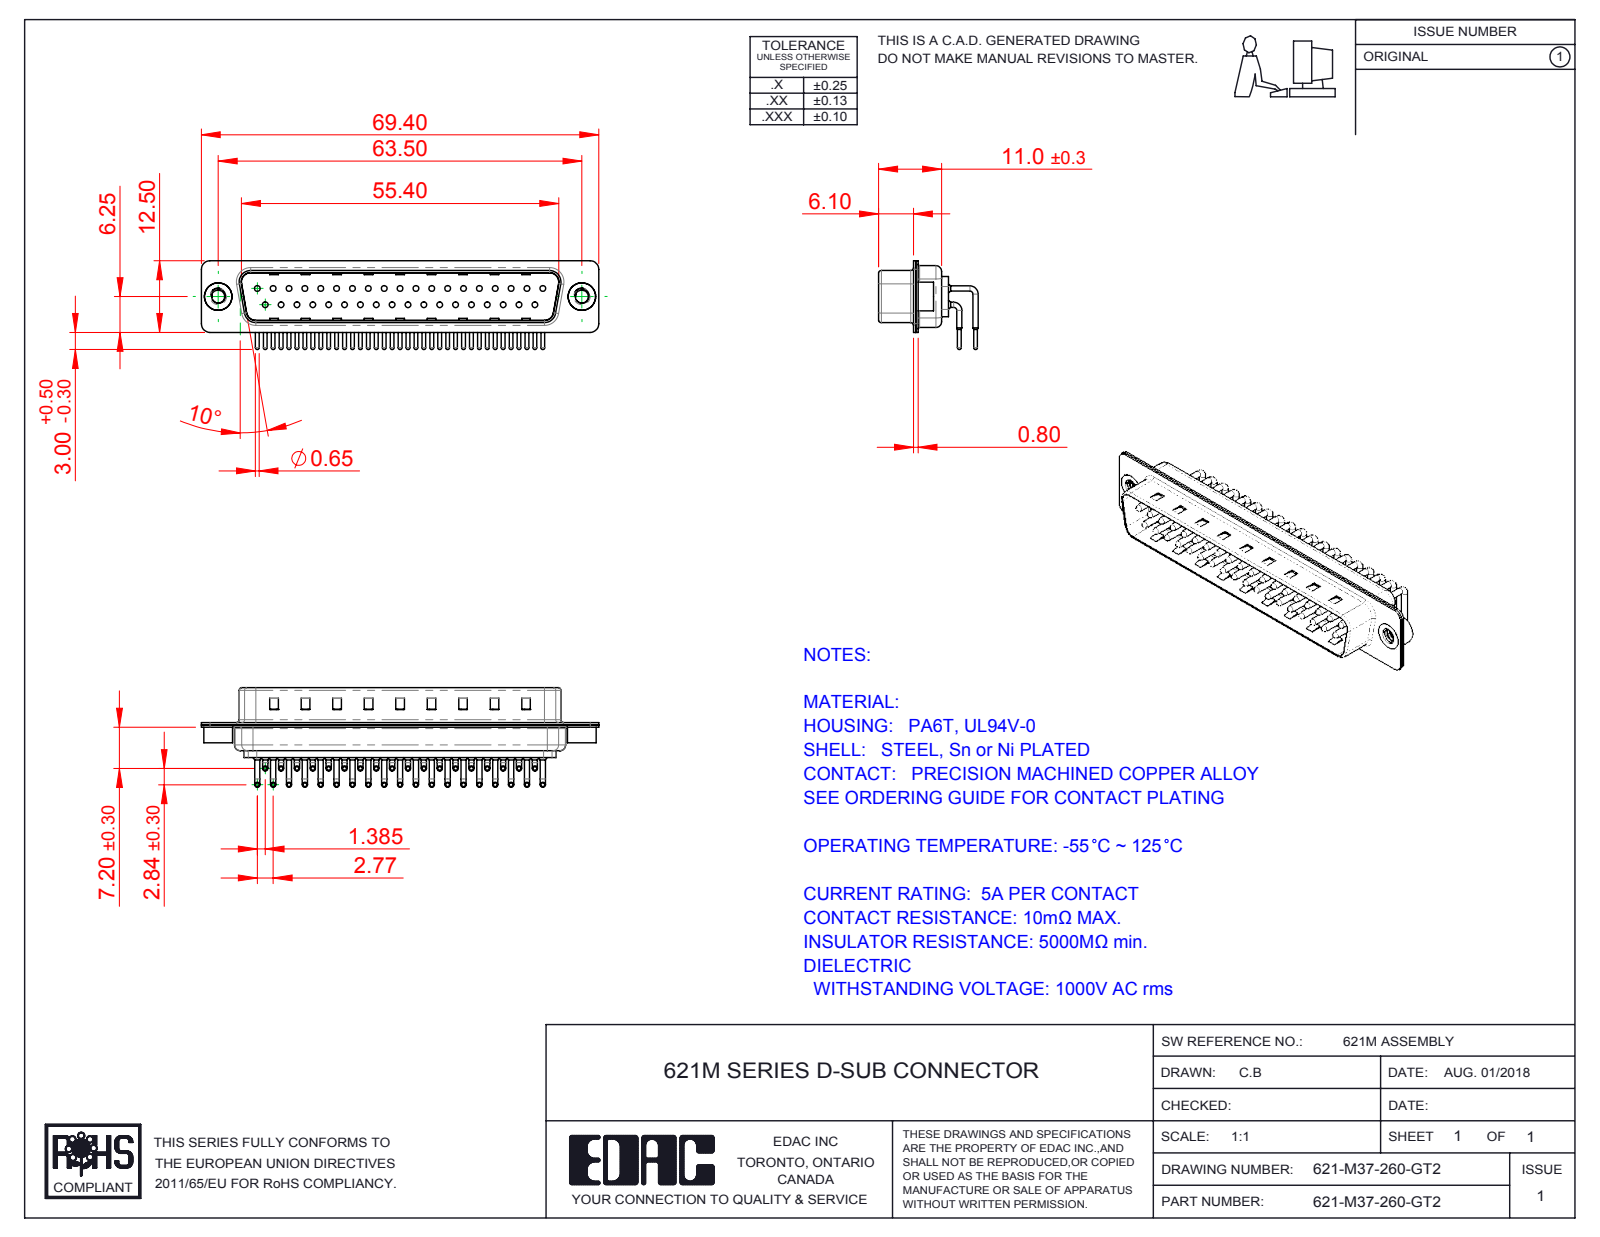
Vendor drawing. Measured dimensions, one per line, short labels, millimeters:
name: 621-M37-260-GT2; 621M Shell Rear_37 Contacts; 621M 4-40 Threaded Rivet; 621M Shell Front_37 Contacts (+3 more)
written by: SolidWorks 2016 (CONFIG_CONTROL_DESIGN)
unit: mm
bodies: 42 solids, 4482 faces (2571 planar, 1473 cylindrical, 438 other)
size: 69.4 × 17.39 × 15.49
volume: 3 997 mm³; area: 10 368 mm²
holes: 37× ⌀1, 37× ⌀1.7, 37× ⌀2, 2× ⌀2.26, 2× ⌀4, 2× ⌀4.8
bosses: 74× ⌀0.9, 37× ⌀1.5, 37× ⌀0.65, 2× ⌀5, 2× ⌀4.9
rounds: 37× R1.01, 16× R1.5, 12× R2, 8× R0.5, 8× R1.6, 4× R0.25, 4× R0.6, 4× R0.65
face distances: 0.4, 0.85, 9.55, 8.7, 1.25, 10.4, 1.5, 1.9, 0.35, 9.95
hole spacings: 3.16, 2.77, 5.54, 8.31, 5.04, 10.1, 11.08, 12.78
